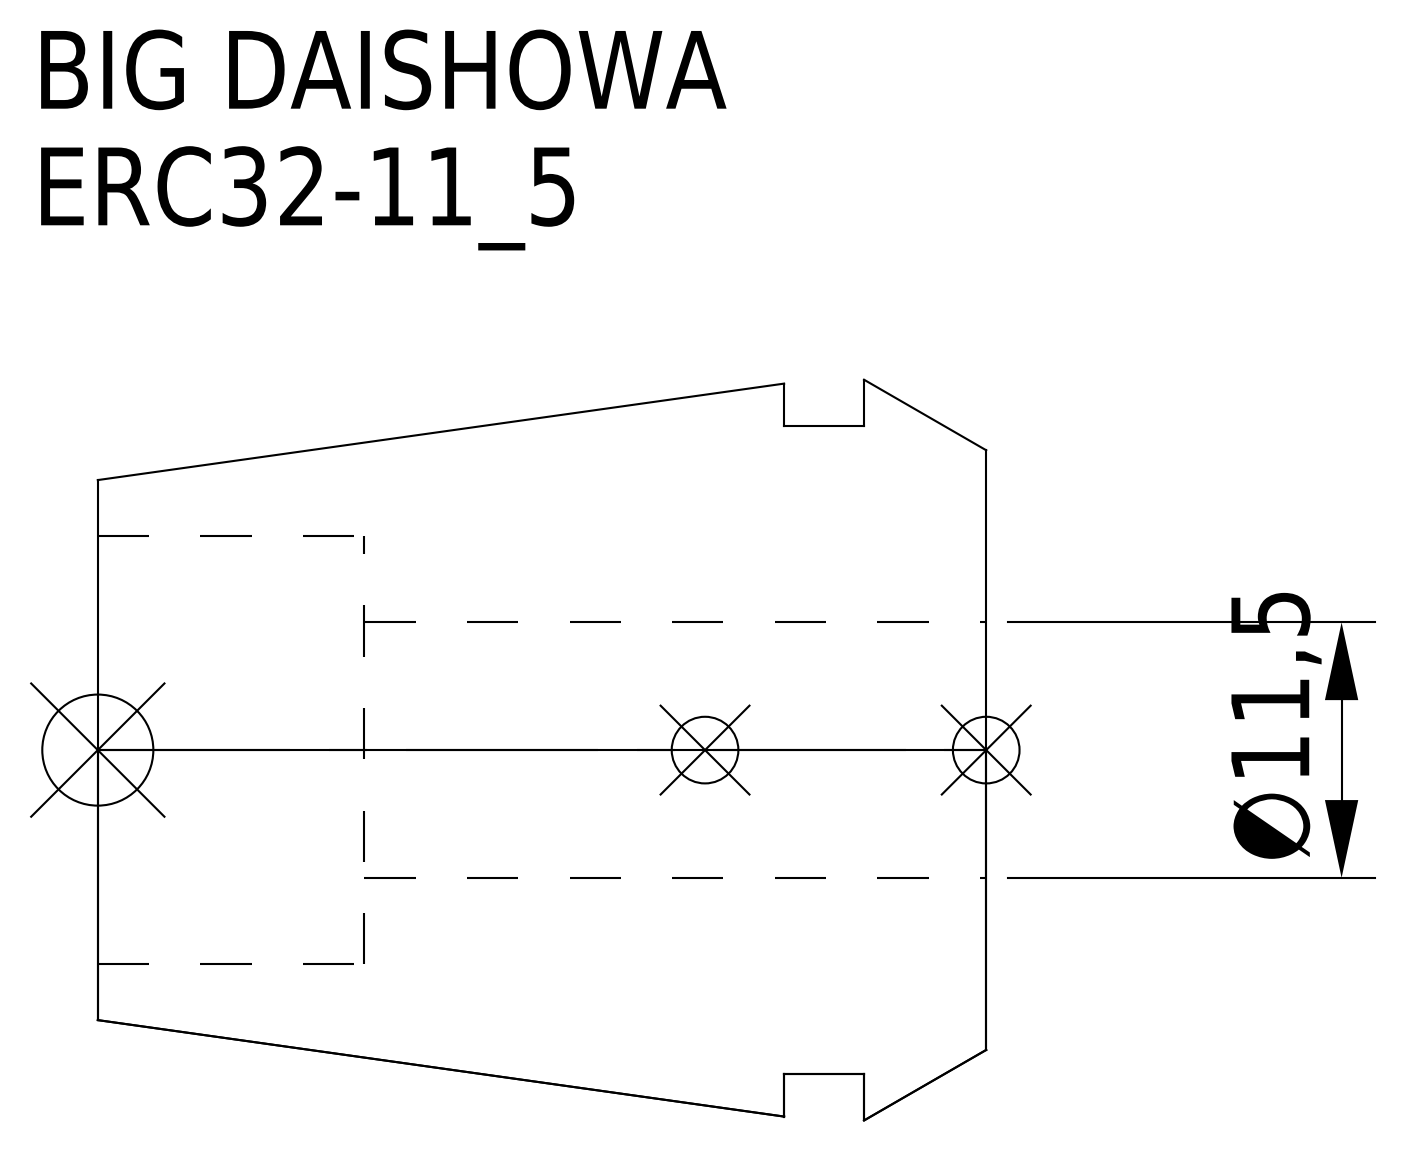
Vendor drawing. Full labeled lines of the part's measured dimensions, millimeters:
Part name (STEP PRODUCT): ERC32-11_5
STEP written by: CREO PARAMETRIC BY PTC INC, 2016380 (AUTOMOTIVE_DESIGN)
Units: millimetres
Bodies: 1 solid, 15 faces (5 planar, 6 cylindrical, 4 other)
Overall size (bounding box): 40 × 33.35 × 33.35
Volume: 20 023 mm³ · Surface area: 6 699 mm²
Round holes (diameter × count): ⌀11.5 ×1, ⌀19.3 ×1
Round bosses / shafts (diameter × count): ⌀29.2 ×1
Main face-to-face distances: 5.5, 28, 22.5, 9.1, 3.6, 18.9, 40, 34.5, 30.9, 12
